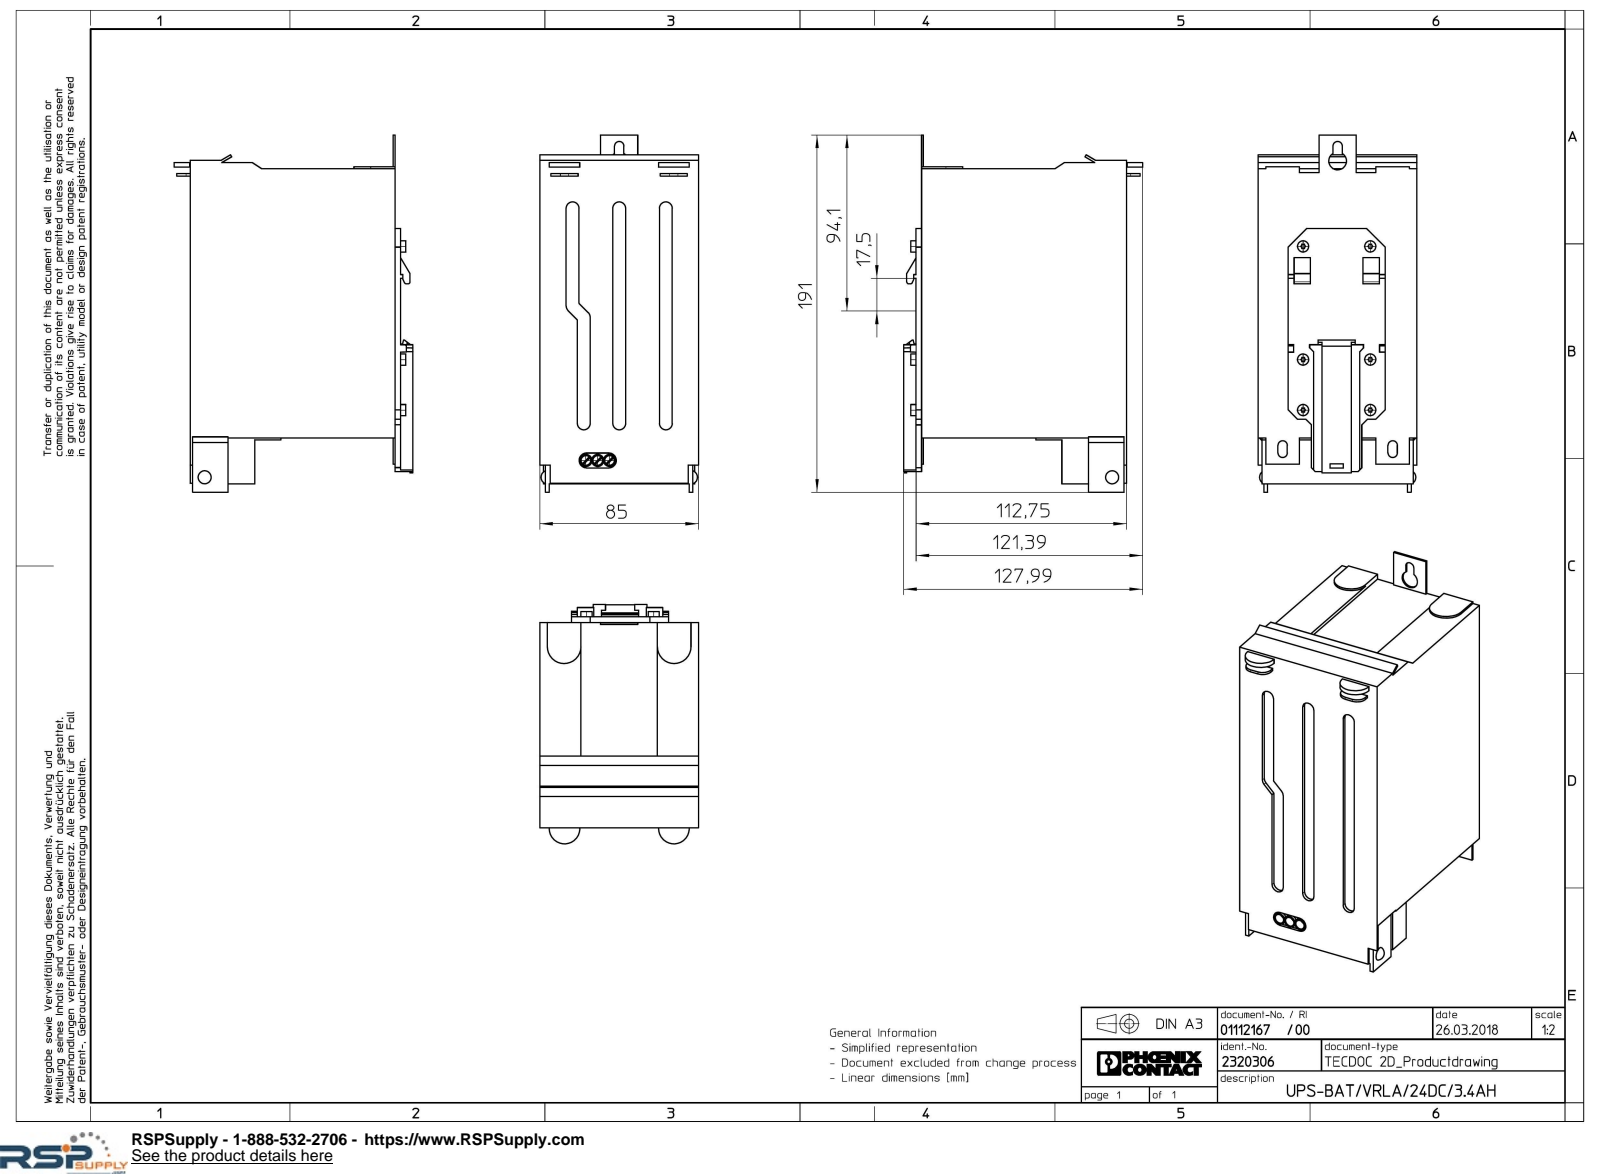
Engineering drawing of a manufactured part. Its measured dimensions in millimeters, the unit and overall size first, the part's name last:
Units: millimetres
Overall size (bounding box): 191 × 127.99 × 85
Round holes (diameter × count): ⌀5.2 ×3, ⌀9.5 ×1
Round bosses / shafts (diameter × count): ⌀6 ×6
Partial cylindrical surfaces — rounded edges, fillets, slot ends (radius × count): R1.3 ×36, R3.45 ×8, R2.5 ×5, R5 ×4, R3.25 ×3, R0.55 ×2, R1 ×2, R4 ×2
Main face-to-face distances: 85, 109.75, 2, 3, 112.75, 1, 142, 110.75, 107.75, 144
Hole centre spacings: 6.35, 12.7, 160.13, 160.46, 161.04
Volume: 1 444 000 mm³ · Surface area: 92 943 mm²
Bodies: 1 solid, 370 faces (276 planar, 90 cylindrical, 4 other)
Part name (STEP PRODUCT): UPS_BAT_VRLA_24DC_3.4AH-select
STEP written by: Creo Elements/Direct Modeling 20.1A 29-Sep-2018 (C) Parametric Technology GmbH (AUTOMOTIVE_DESIGN)
